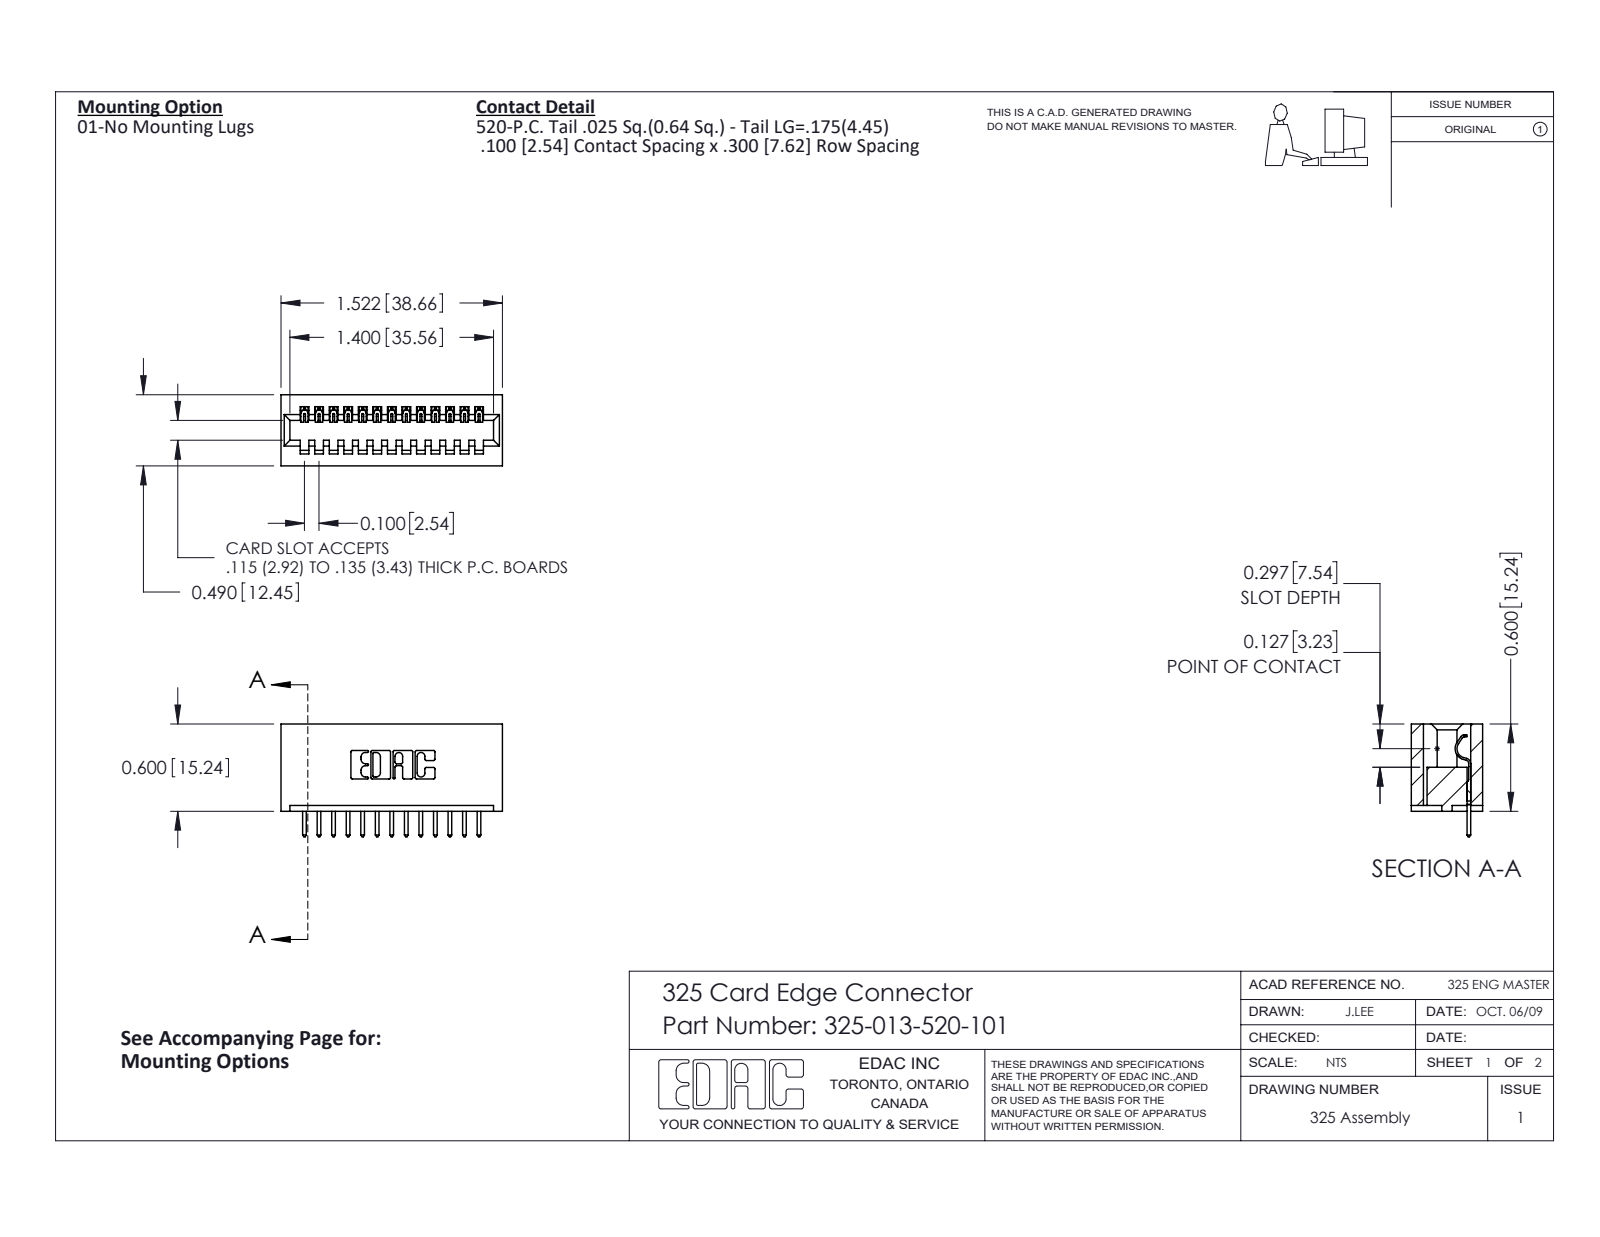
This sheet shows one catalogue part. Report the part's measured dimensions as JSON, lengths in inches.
{"part_name": "325 Part_Lugless; 325-013-520-101; 325-292-001_325-293-120", "step_written_by": "SolidWorks 2016 (CONFIG_CONTROL_DESIGN)", "units": "inches", "bodies": {"solids": 14, "faces": 860, "planar": 612, "cylindrical": 248, "other": 0}, "overall_size": [1.522, 0.775, 0.49], "volume_in3": 0.318, "surface_area_in2": 8.621, "partial_cylinders_radius": [[0.006, 26], [0.01, 26], [0.01, 22], [0.007, 6], [0.031, 6], [0.026, 3], [0.014, 1], [0.022, 1]], "face_to_face_distances": [0.083, 0.407, 0.3, 0.1, 0.49, 0.2, 0.6, 0.4, 0.56, 0.06]}
